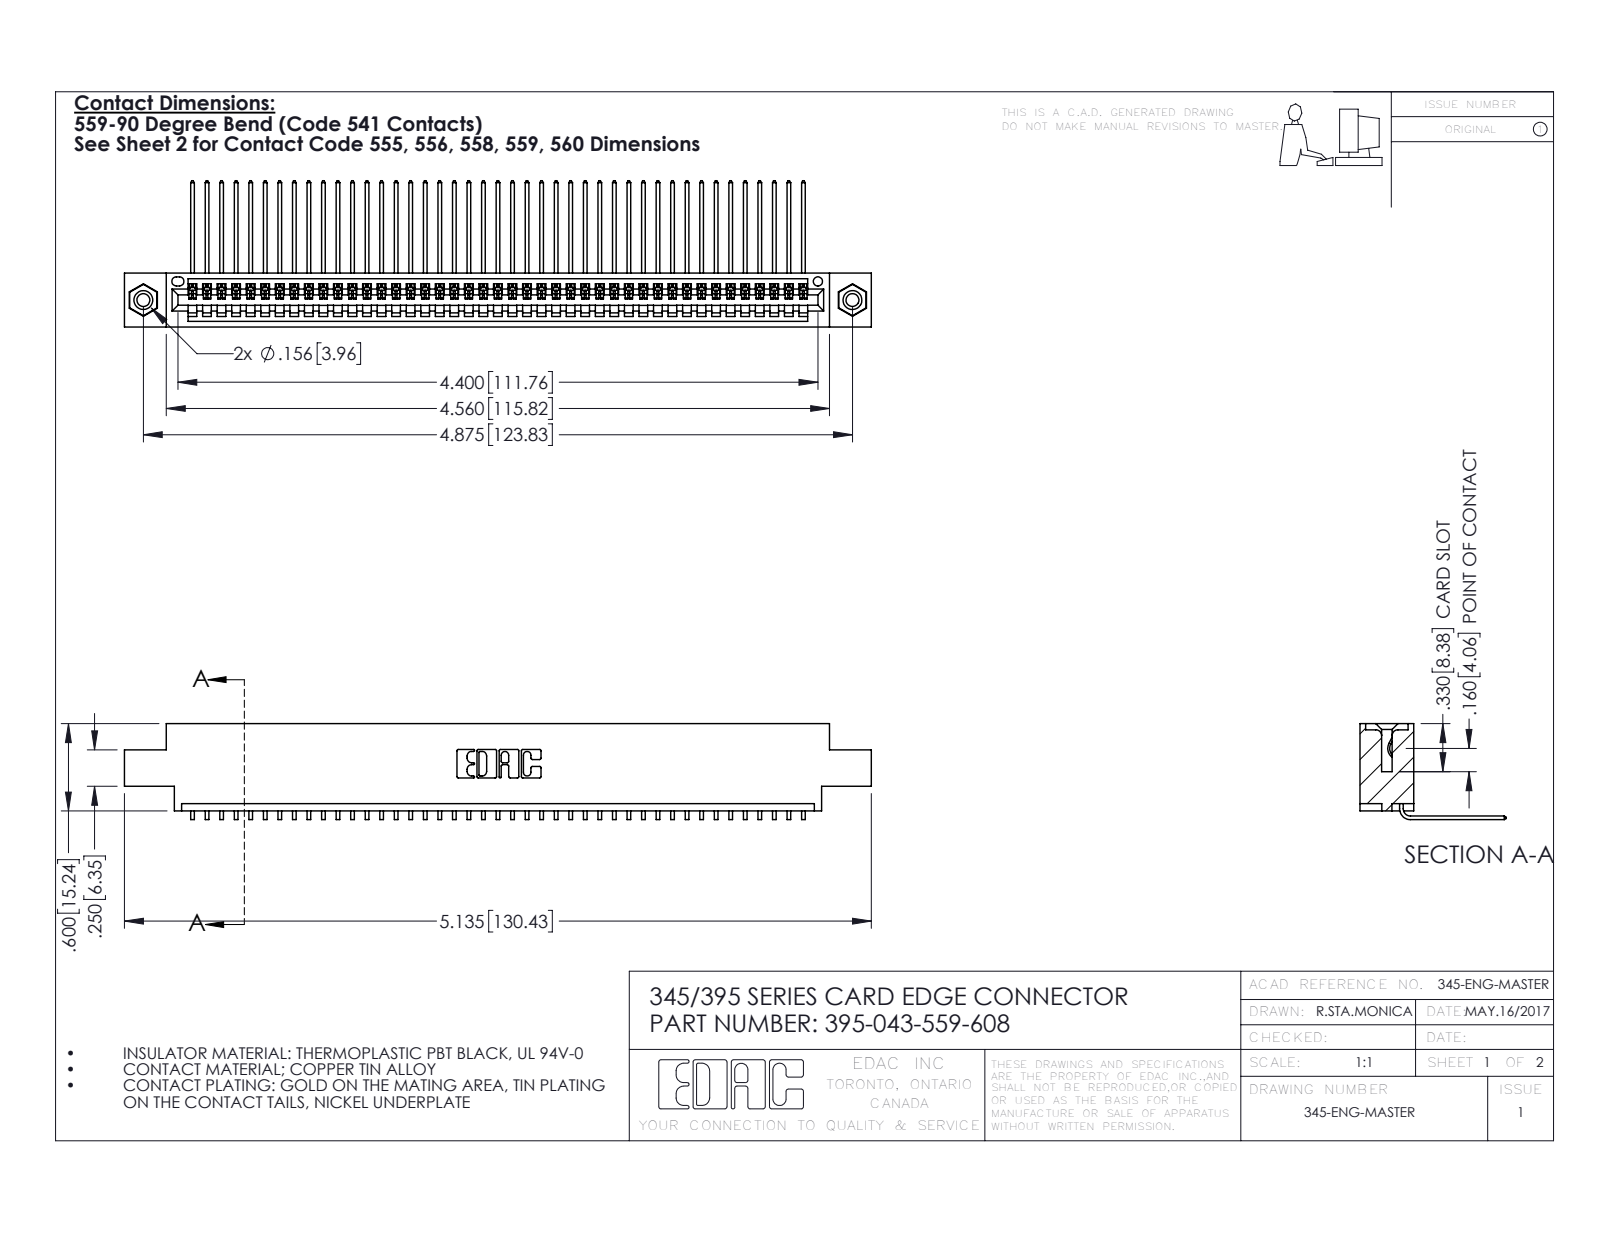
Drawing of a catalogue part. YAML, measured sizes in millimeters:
part_name: "395-043-559-608; 345 Part_0.170 Offset - 0.156 Dia-TI; 345-250-001_345-250-003-102; 345-292-001_558 559 Tail - 1"
step_written_by: "SolidWorks 2016 (CONFIG_CONTROL_DESIGN)"
units: millimeters
bodies: {solids: 46, faces: 2770, planar: 1922, cylindrical: 832, other: 16}
overall_size: [130.4, 25.5, 16.7]
volume: 12400
surface_area: 17500
round_holes:
  - {diameter: 2.3, count: 2}
  - {diameter: 3.2, count: 2}
  - {diameter: 4, count: 2}
  - {diameter: 1.6, count: 1}
round_bosses_or_shafts:
  - {diameter: 3.9, count: 2}
partial_cylinders:
  - {radius: 0.2, count: 86}
  - {radius: 0.3, count: 22}
  - {radius: 0.2, count: 6}
  - {radius: 0.8, count: 6}
  - {radius: 0.7, count: 3}
  - {radius: 0.8, count: 2}
  - {radius: 1, count: 2}
  - {radius: 0.4, count: 1}
face_to_face_distances: [1.8, 7.6, 9.4, 5.1, 2.5, 6.9, 0.6, 5.7, 4.4, 3.8]
hole_center_spacings: [6.9, 117.8, 123.8]
